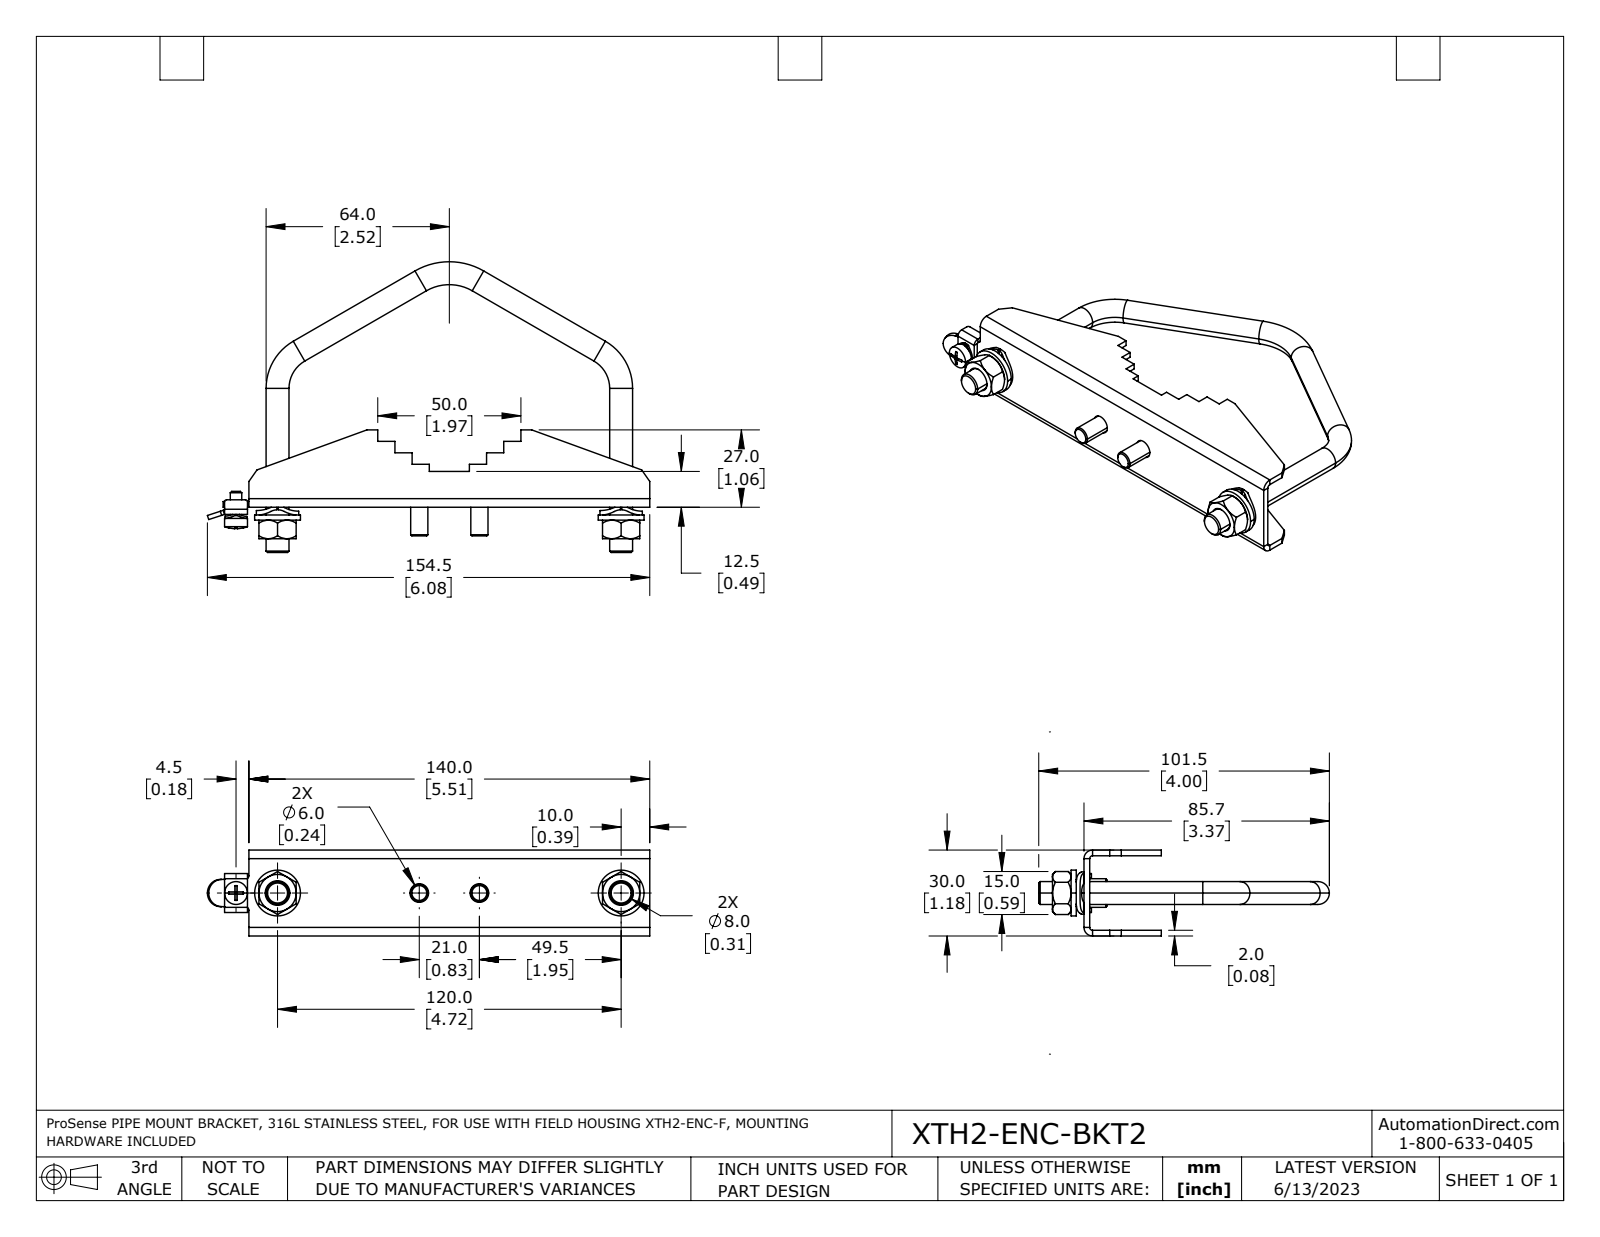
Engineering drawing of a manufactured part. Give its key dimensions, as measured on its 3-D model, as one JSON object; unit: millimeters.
{"part_name": "XATMT-71597448", "step_written_by": "SolidWorks 2021 (AUTOMOTIVE_DESIGN)", "units": "millimeters", "bodies": {"solids": 2, "faces": 355, "planar": 154, "cylindrical": 132, "other": 69}, "overall_size": [154.5, 101.5, 30], "volume_mm3": 34710, "surface_area_mm2": 28730, "round_holes": [[6.5, 2], [8.1, 2], [8.4, 2], [9, 2], [4.2, 1], [4.3, 1]], "round_bosses_or_shafts": [[8, 5], [16, 2], [14.8, 2], [10, 2], [6, 2], [7.6, 1], [4, 1]], "partial_cylinders_radius": [[0.2, 12], [1, 6], [10.6, 6], [5, 4], [5.3, 3], [0.3, 2], [0.7, 2], [1.8, 2]], "face_to_face_distances": [2, 28, 26, 30, 13, 6.5, 4.7, 2.7, 4.5, 11], "hole_center_spacings": [49.5, 70.5, 14.5, 21, 64, 85, 120, 134.5]}
